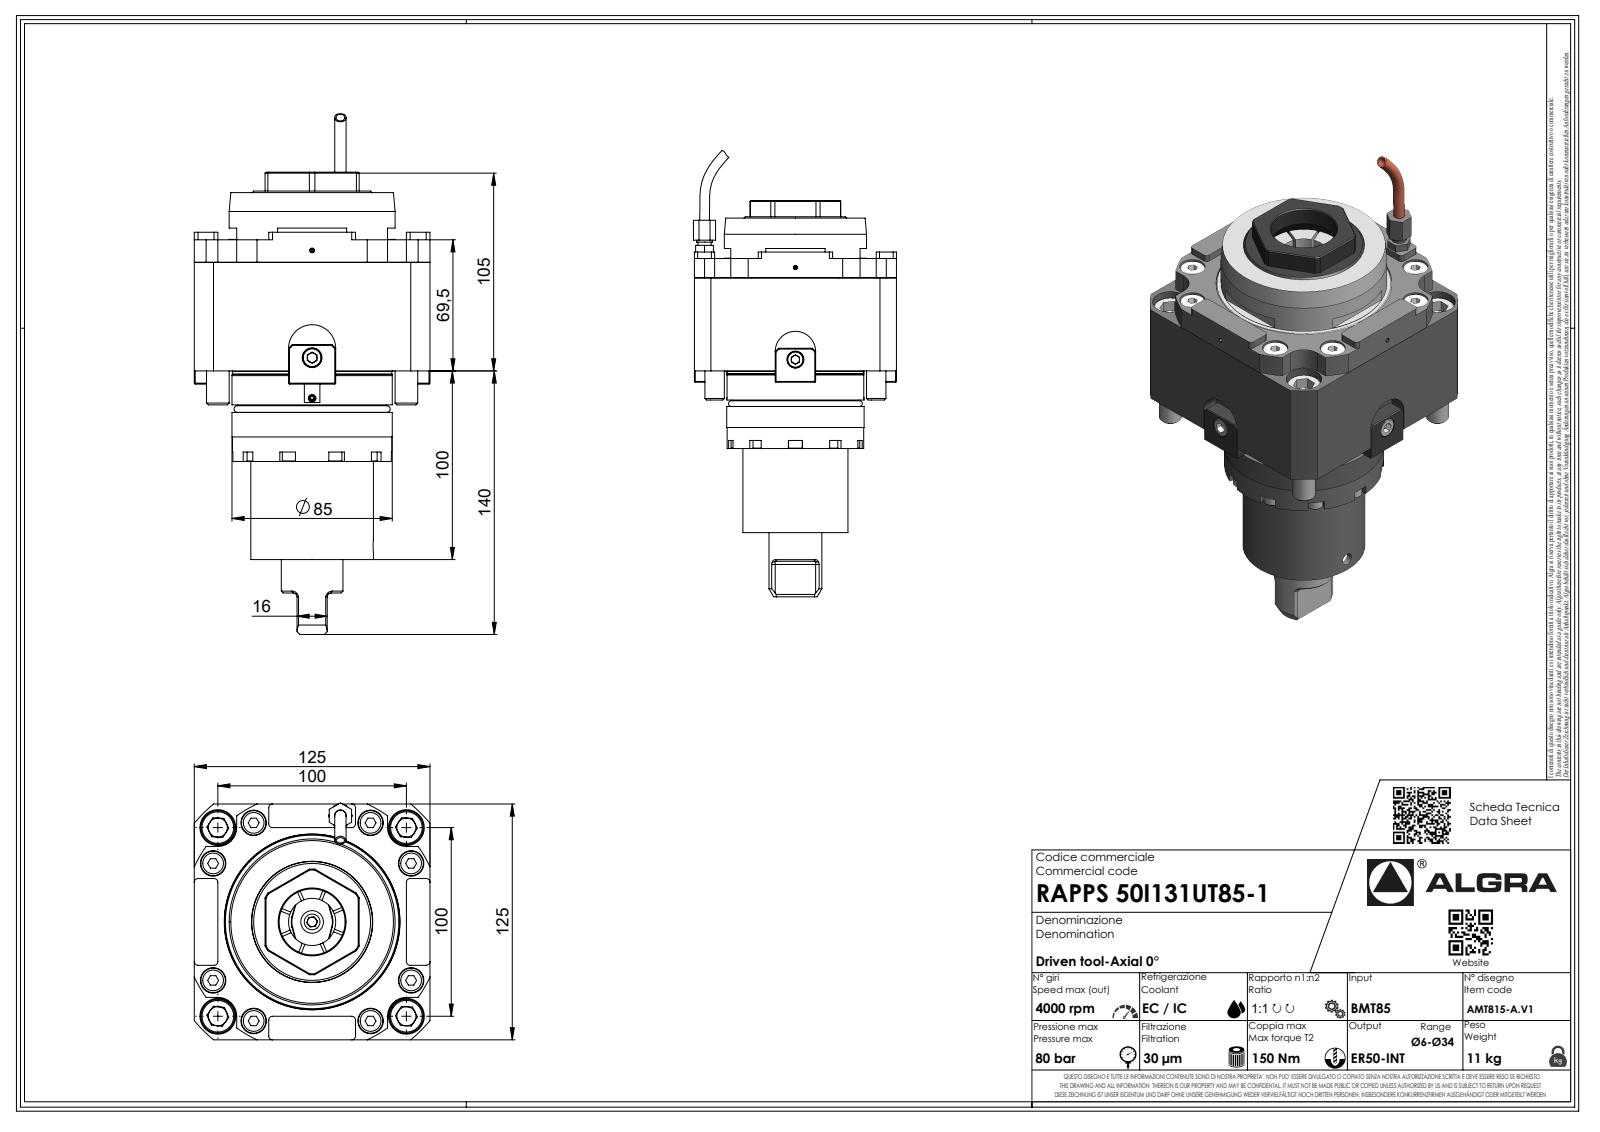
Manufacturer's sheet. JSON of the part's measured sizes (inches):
{"part_name": "RAPPS50I131UT85-1", "step_written_by": "SolidWorks 2023 (AUTOMOTIVE_DESIGN)", "units": "inches", "bodies": {"solids": 1, "faces": 597, "planar": 393, "cylindrical": 80, "other": 124}, "overall_size": [10.866, 4.944, 4.921], "volume_in3": 104.9, "surface_area_in2": 167.2, "round_holes": [[0.083, 1]], "round_bosses_or_shafts": [[0.472, 4], [3.465, 1], [3.346, 1], [2.559, 1], [1.287, 1], [0.386, 1], [0.321, 1], [0.251, 1]], "partial_cylinders_radius": [[0.079, 22], [0.013, 7], [0.02, 7], [0.146, 7], [0.394, 4], [0.008, 1], [1.102, 1], [2.717, 1]], "face_to_face_distances": [4.921, 2.736, 1.89, 0.984, 3.937, 3.72, 6.673, 7.657, 2.047, 4.626]}
